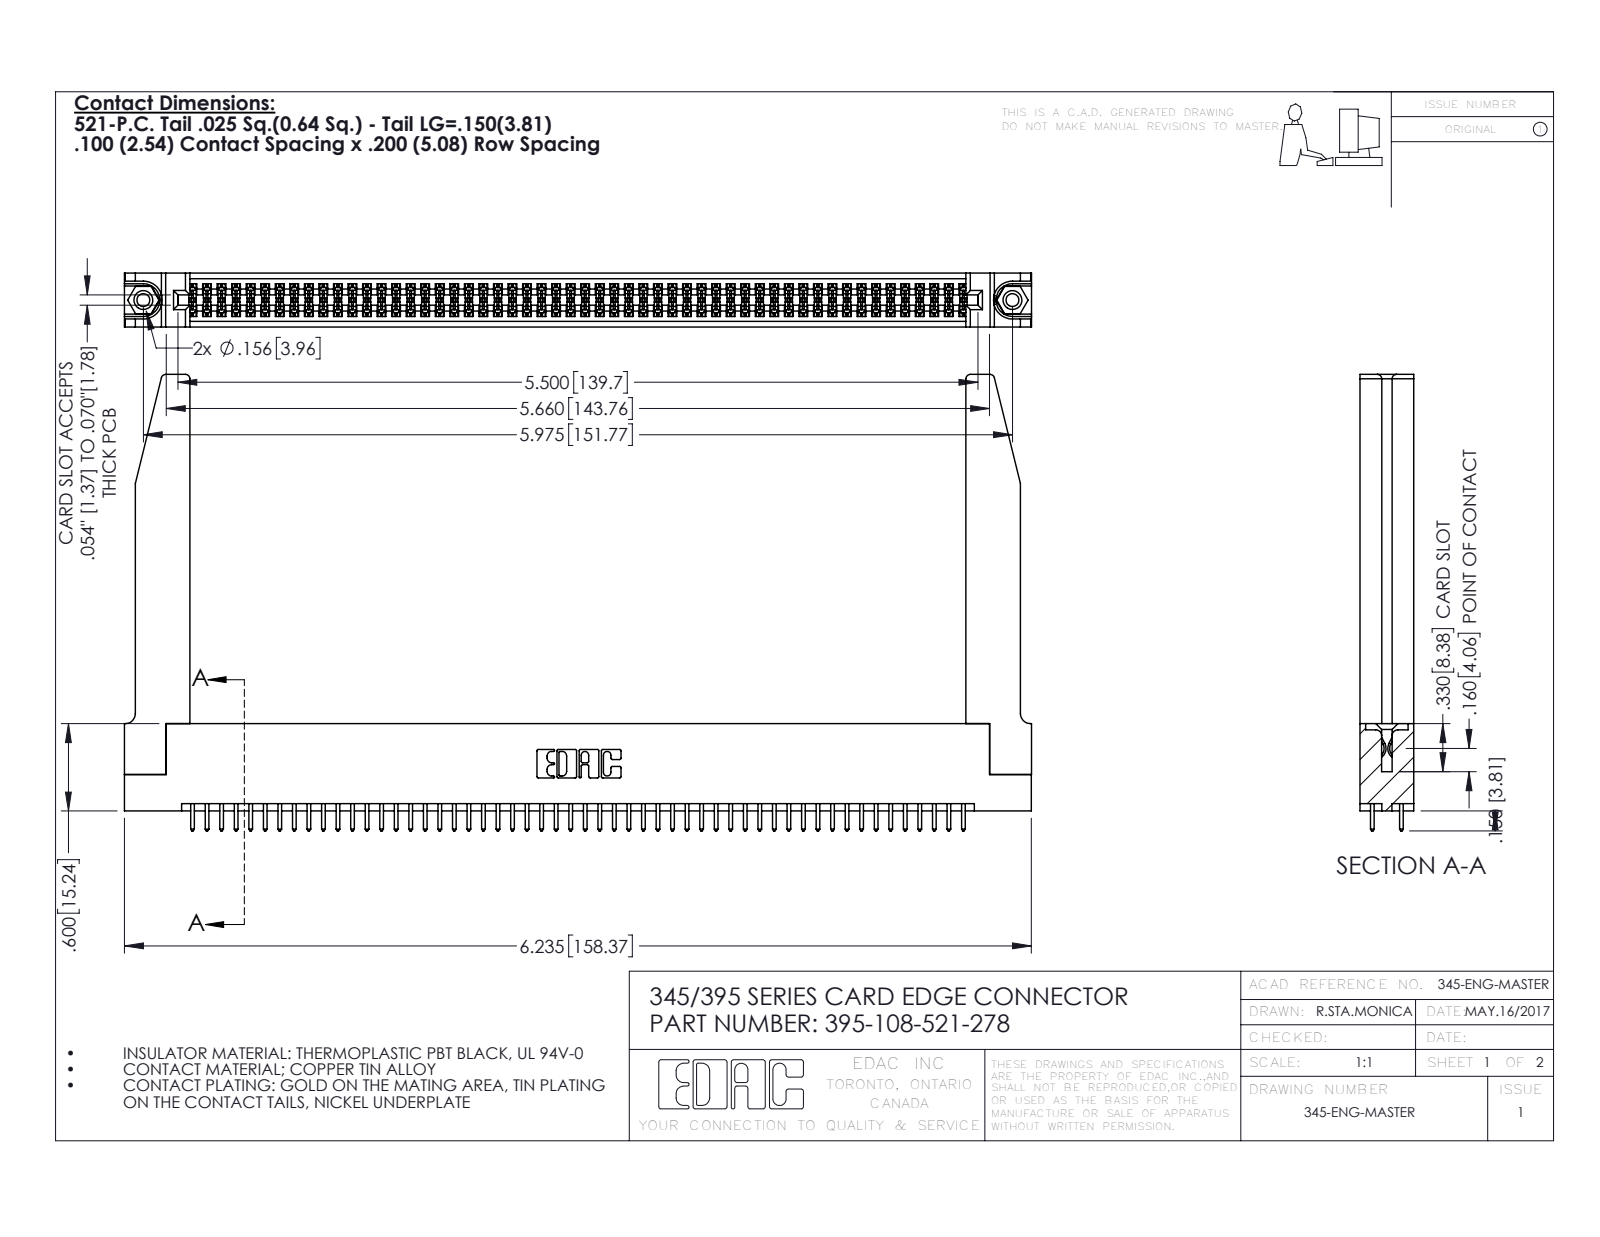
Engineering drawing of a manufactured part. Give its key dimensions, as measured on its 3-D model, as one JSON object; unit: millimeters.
{"part_name": "345 Part_Flush Mounting Lugs - 0.156 Dia-TH; 345-292-001_345-293-121; 345-250-001_345-250-001-102; 345-220-078_345-220-078 (+1 more)", "step_written_by": "SolidWorks 2016 (CONFIG_CONTROL_DESIGN)", "units": "millimeters", "bodies": {"solids": 113, "faces": 5760, "planar": 3786, "cylindrical": 1922, "other": 52}, "overall_size": [158.4, 79.7, 9.4], "volume_mm3": 23220, "surface_area_mm2": 29630, "round_holes": [[2.3, 2], [3.2, 2], [4, 2], [1.6, 1]], "round_bosses_or_shafts": [[3.9, 2]], "partial_cylinders_radius": [[0.2, 162], [0.3, 108], [0.3, 22], [0.8, 8], [0.2, 6], [0.8, 6], [0.7, 3], [0.4, 2]], "face_to_face_distances": [1.8, 7.6, 9.4, 5.1, 2.5, 6.9, 0.6, 5.7, 4.4, 3.8], "hole_center_spacings": [6.9, 145.8, 151.8]}
